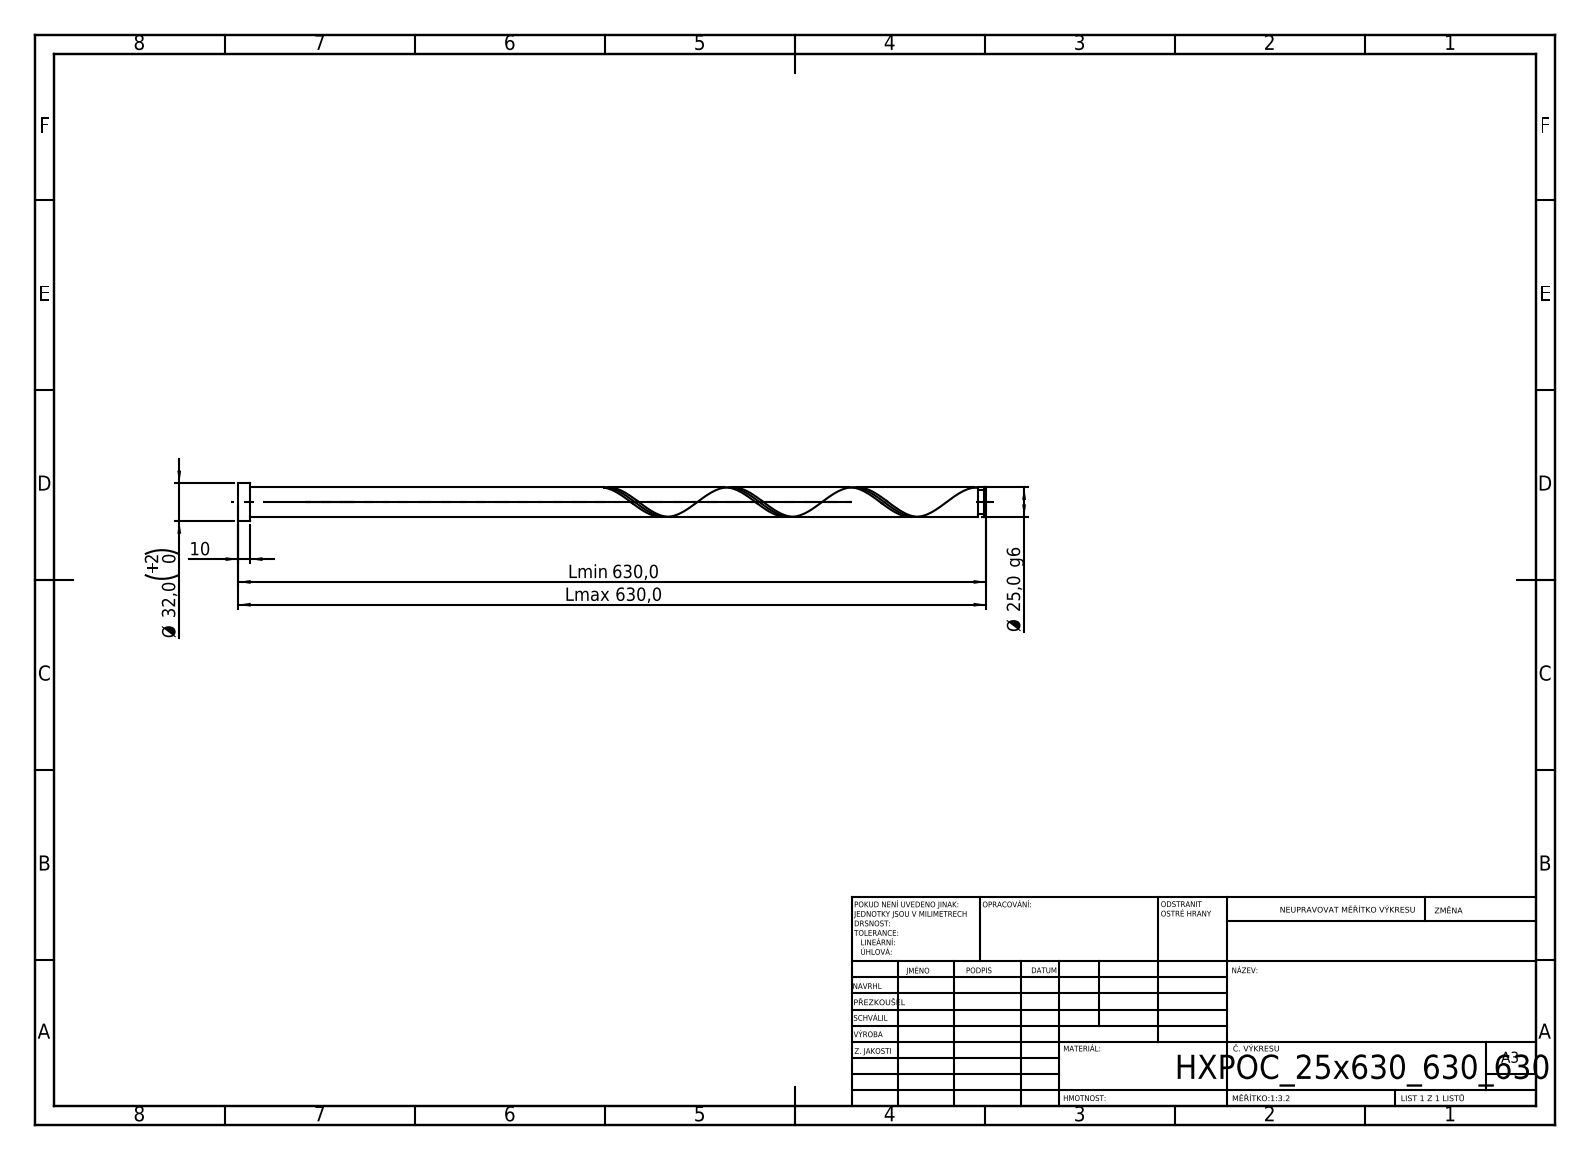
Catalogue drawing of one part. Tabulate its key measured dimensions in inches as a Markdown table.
| quantity | value |
| --- | --- |
| STEP written by | SolidWorks 2019 (CONFIG_CONTROL_DESIGN) |
| units | inches |
| bodies | 1 solid, 21 faces (6 planar, 14 cylindrical, 1 other) |
| overall size | 24.803 × 1.26 × 1.26 |
| volume | 18.83 in³ |
| surface area | 81.53 in² |
| round bosses / shafts (diameter × count) | 1.26 × 1, 0.984 × 1, 0.787 × 1 |
| main face-to-face distances | 24.803, 0.394, 24.409, 24.721, 24.327, 0.082, 24.524, 24.13, 0.197, 0.279 |
